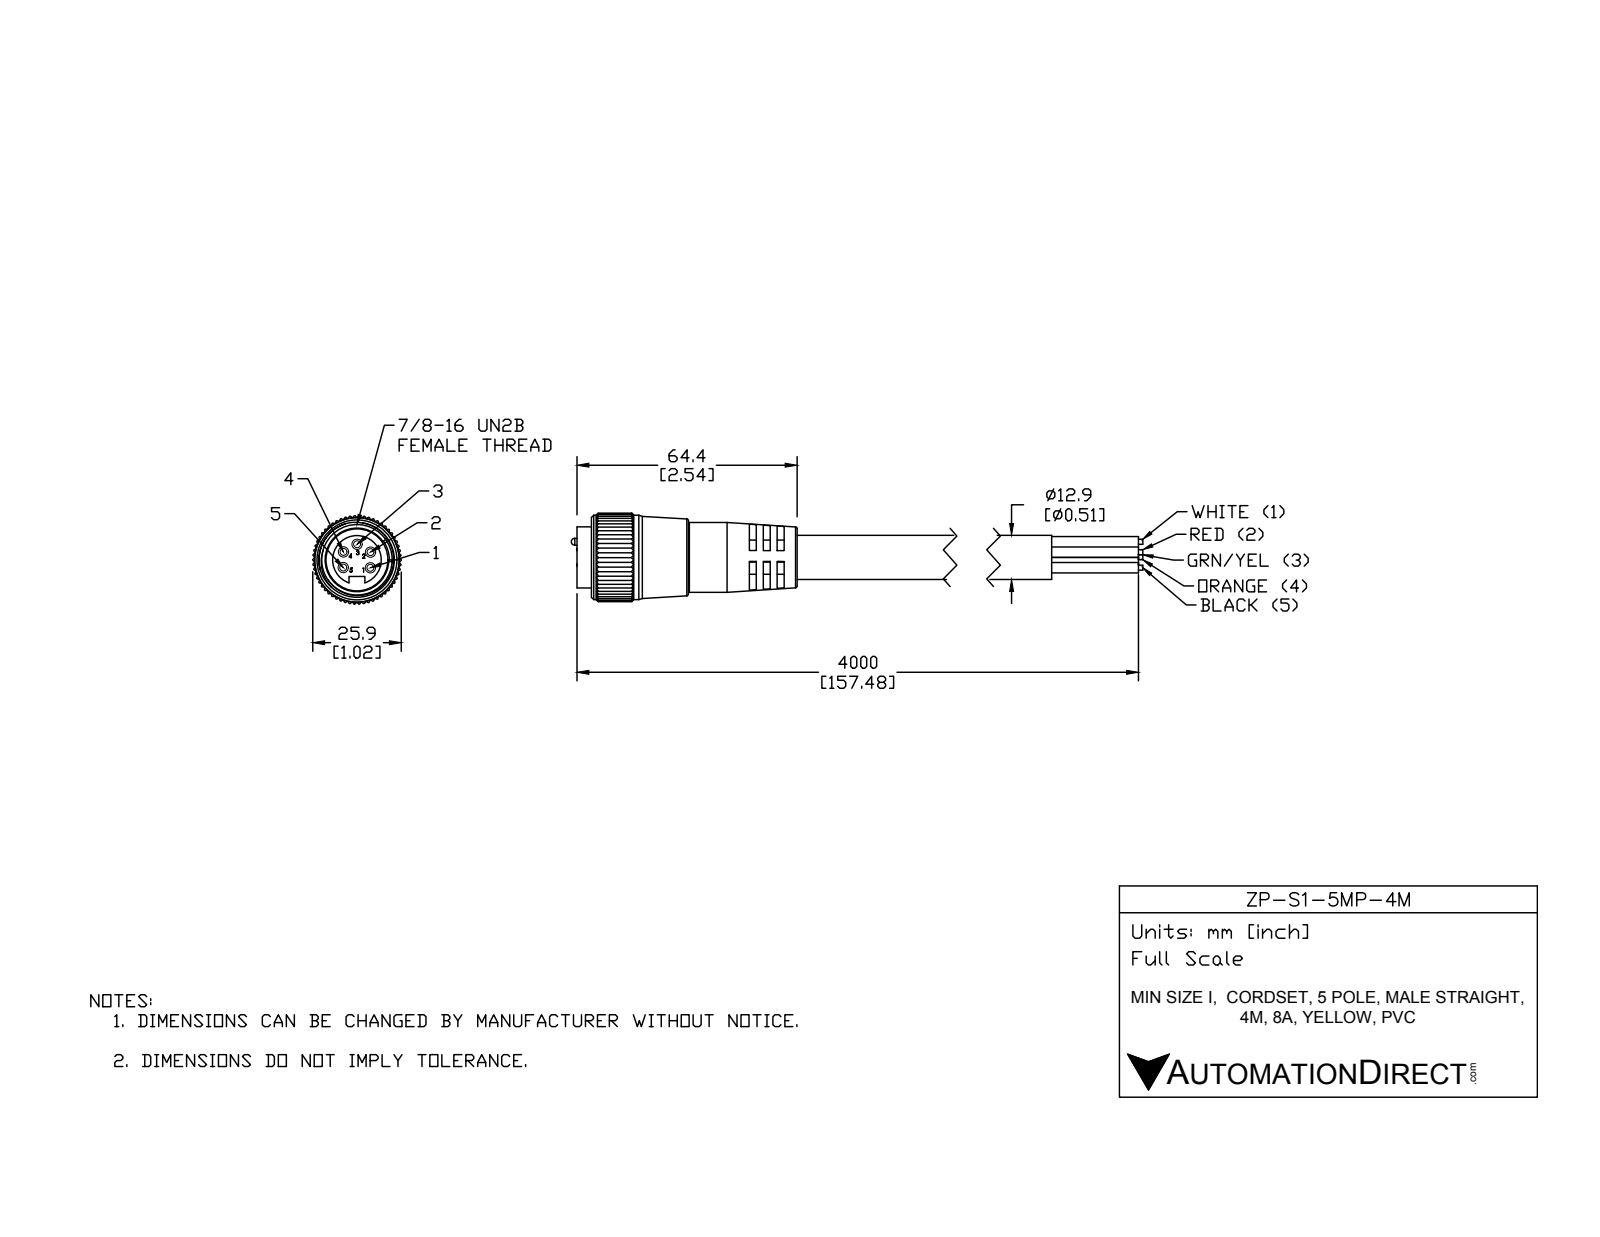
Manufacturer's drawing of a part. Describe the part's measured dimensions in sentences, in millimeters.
The part is named "ZP-S1-5MP-4M". Its 3-D file was written by "SolidWorks 2015 (AUTOMOTIVE_DESIGN)". It is 7 solids with 614 faces: 222 planar, 322 cylindrical and 70 other. Overall it measures 111.14 by 52.91 by 25.84 millimeters. Its volume is 30 938 cubic millimeters and its surface area 13 393 square millimeters. Round holes: 1 of diameter 14.22, 1 of diameter 19.96, 1 of diameter 20.45, 1 of diameter 21. Round bosses or shafts: 5 of diameter 3.05, 5 of diameter 2, 2 of diameter 12.93, 1 of diameter 24.68, 1 of diameter 20.4, 1 of diameter 19.5, 1 of diameter 17.88. Partial cylindrical surfaces (rounded edges, fillets, slot ends): 165 of radius 0.25, 1 of radius 2.29, 1 of radius 5.25, 1 of radius 12.93. The main face-to-face distances are 2, 4.04, 2.04, 6.04, 4.02, 6.06, 8.06, 2.02, 10.07, 8.07.
